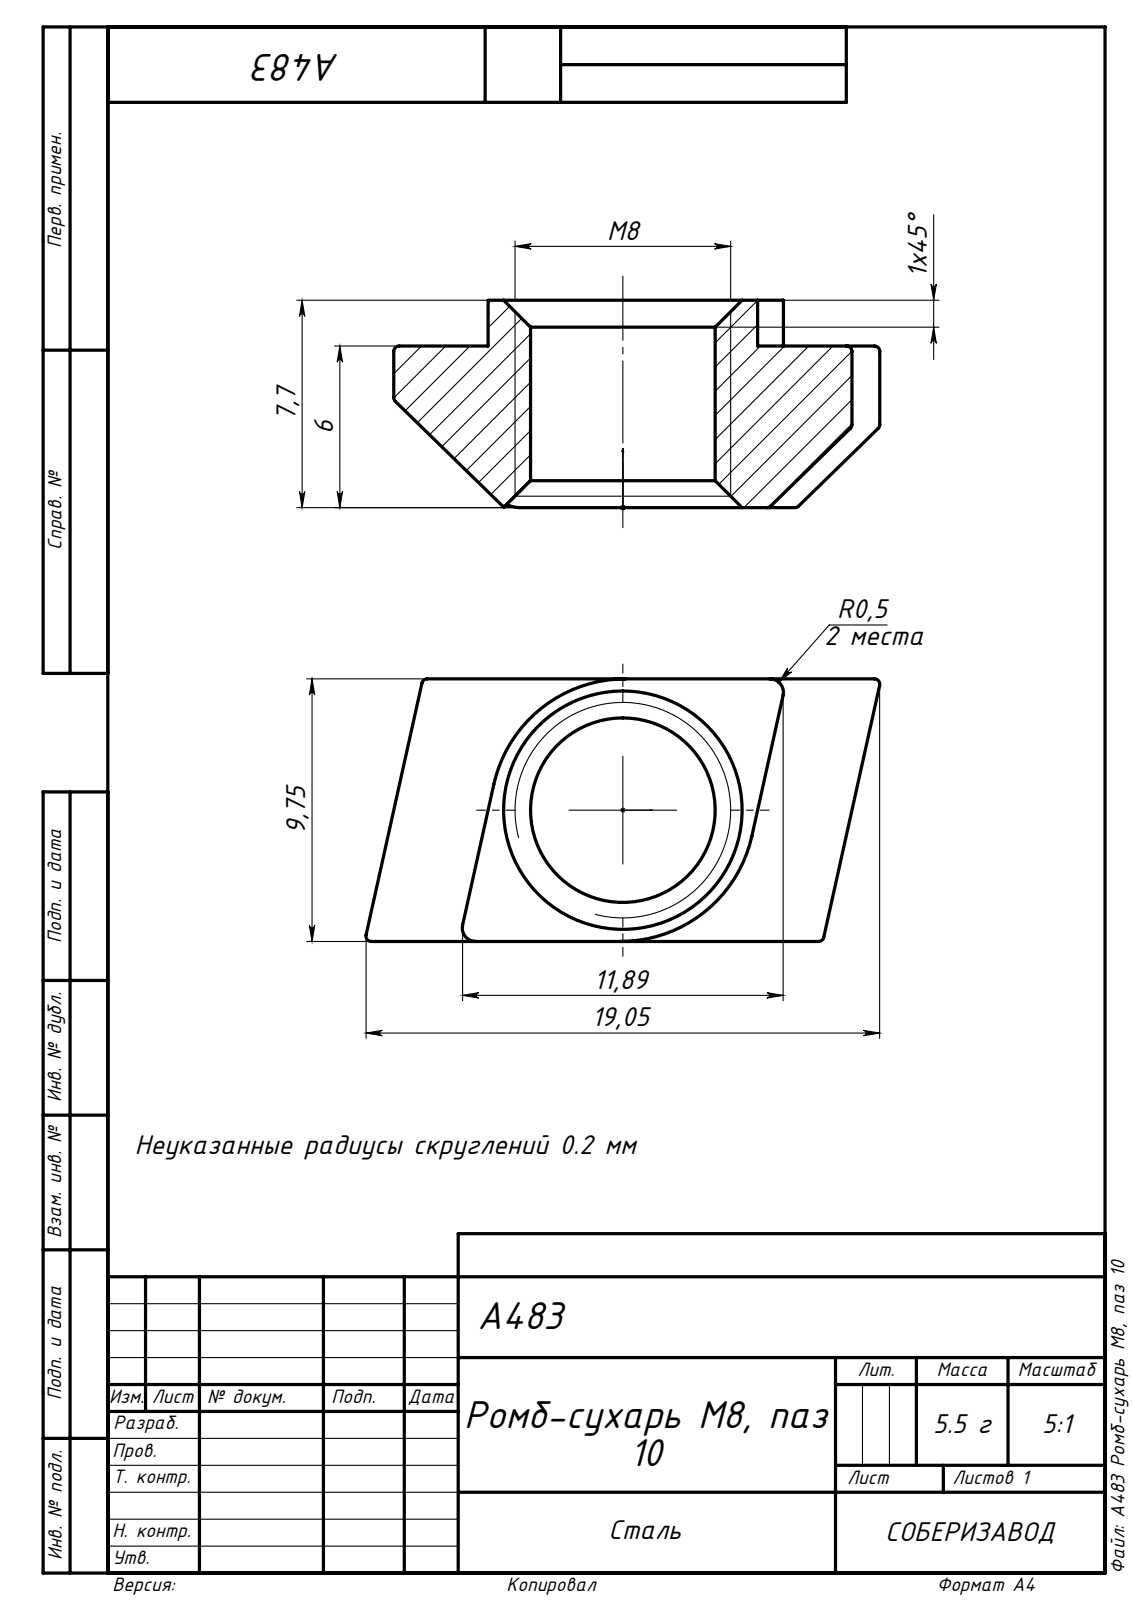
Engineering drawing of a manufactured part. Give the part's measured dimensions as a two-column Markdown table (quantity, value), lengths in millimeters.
| quantity | value |
| --- | --- |
| part name | A483 Ромб-сухарь М8, паз 10 |
| STEP written by | SolidWorks 2021 (AUTOMOTIVE_DESIGN) |
| units | millimeters |
| bodies | 1 solid, 57 faces (12 planar, 28 cylindrical, 17 other) |
| overall size | 19.06 × 9.75 × 7.7 |
| volume | 716 mm³ |
| surface area | 712 mm² |
| round holes (diameter × count) | 6.85 × 1 |
| partial cylindrical surfaces (radius × count) | 0.2 × 18, 0.5 × 2, 5 × 2 |
| main face-to-face distances | 9.75, 1.7, 6, 7.7, 3.42, 13.18, 16.6, 9.76 |
